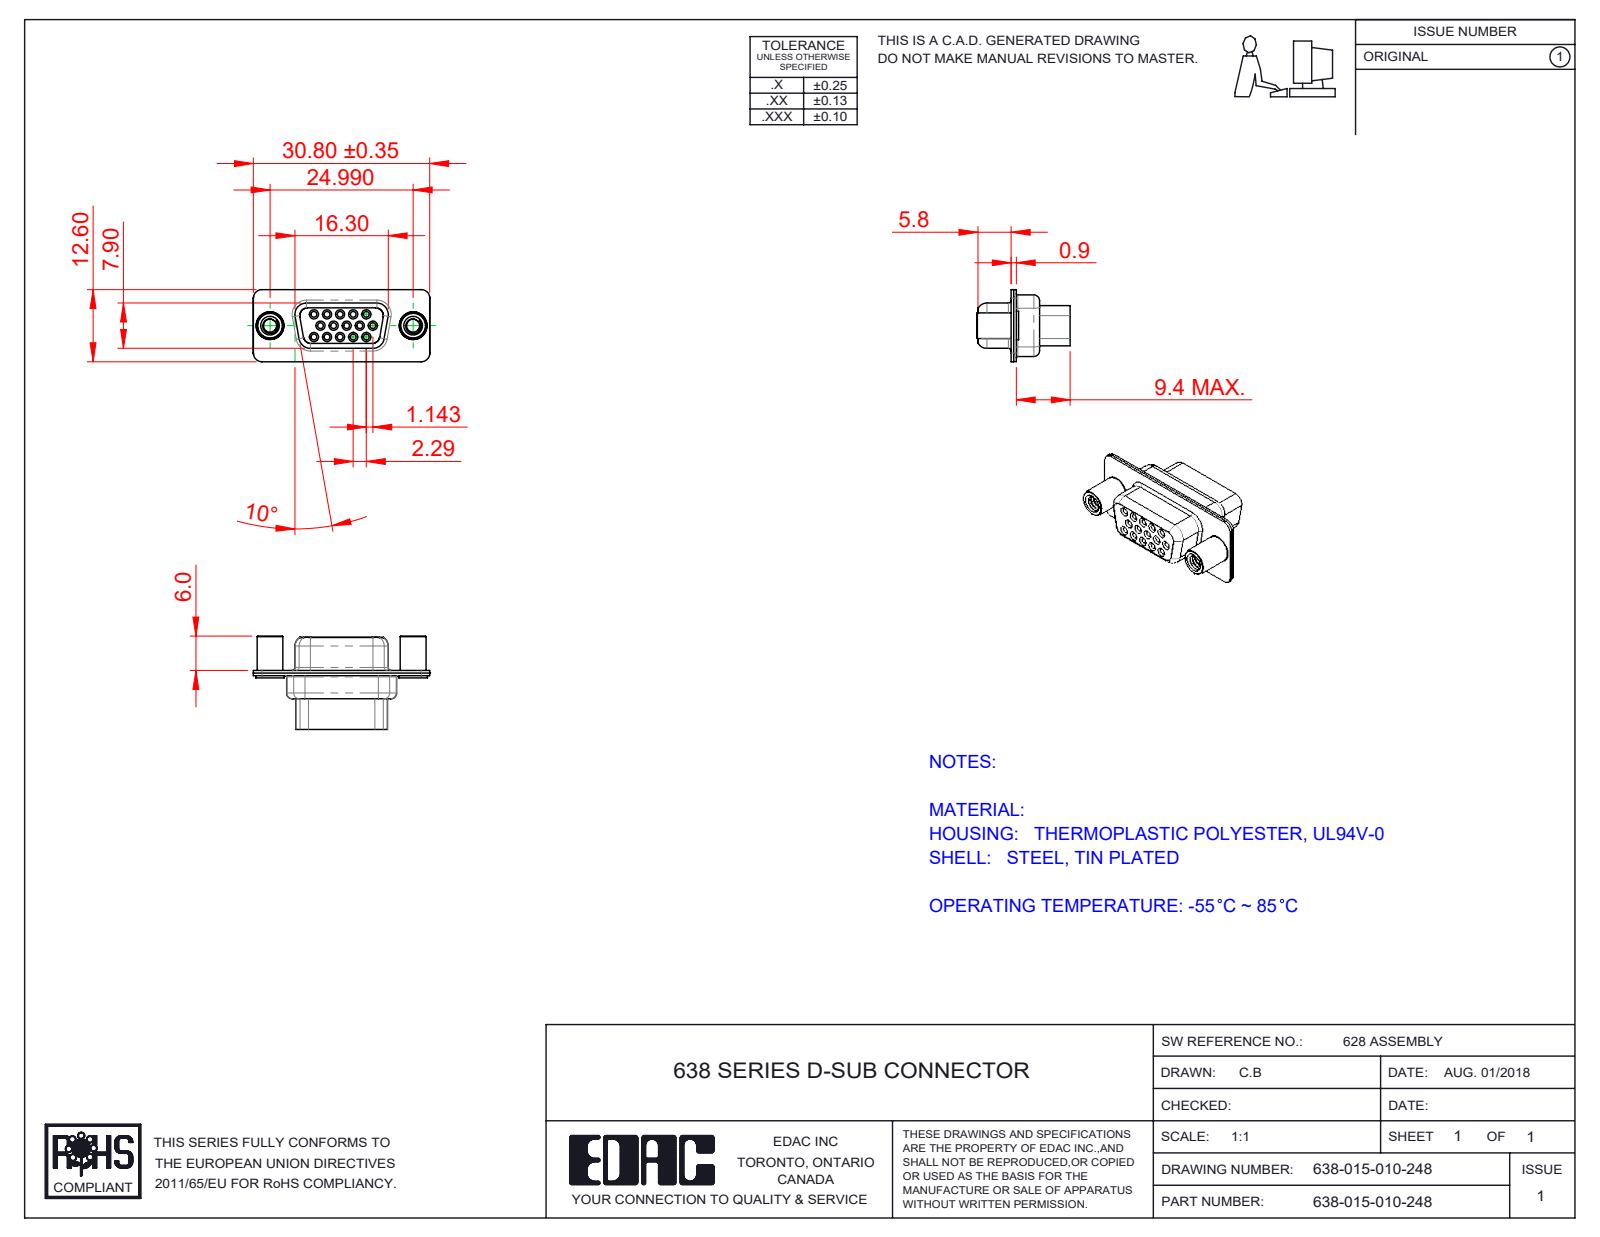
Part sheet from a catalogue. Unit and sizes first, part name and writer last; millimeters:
Units: millimetres
Overall size (bounding box): 30.81 × 16.3 × 12.6
Round holes (diameter × count): ⌀1 ×15, ⌀1.7 ×15, ⌀1.8 ×15, ⌀2 ×15, ⌀2.26 ×2, ⌀4 ×2, ⌀4.05 ×2, ⌀4.85 ×2
Round bosses / shafts (diameter × count): ⌀5 ×2, ⌀4.95 ×2, ⌀4.8 ×2, ⌀4.5 ×2
Partial cylindrical surfaces — rounded edges, fillets, slot ends (radius × count): R1.5 ×20, R2 ×12, R1.55 ×8, R1.35 ×5, R0.25 ×4, R0.5 ×4, R0.55 ×4, R0.7 ×4
Main face-to-face distances: 0.45, 0.9, 0.4, 1.43, 8.88, 6.6, 7, 0.85, 9.4, 6.2
Hole centre spacings: 3.96, 2.28, 4.57, 2.29, 6.05, 6.86, 7.92, 6.04
Volume: 1 774 mm³ · Surface area: 4 743 mm²
Bodies: 5 solids, 508 faces (114 planar, 285 cylindrical, 109 other)
Part name (STEP PRODUCT): 638-015-010-248; 638 Housing_15 Contacts HP; 638 4-40 Threaded Standoff; 638 Shell Front_15 Contacts (+1 more)
STEP written by: SolidWorks 2020 (CONFIG_CONTROL_DESIGN)
